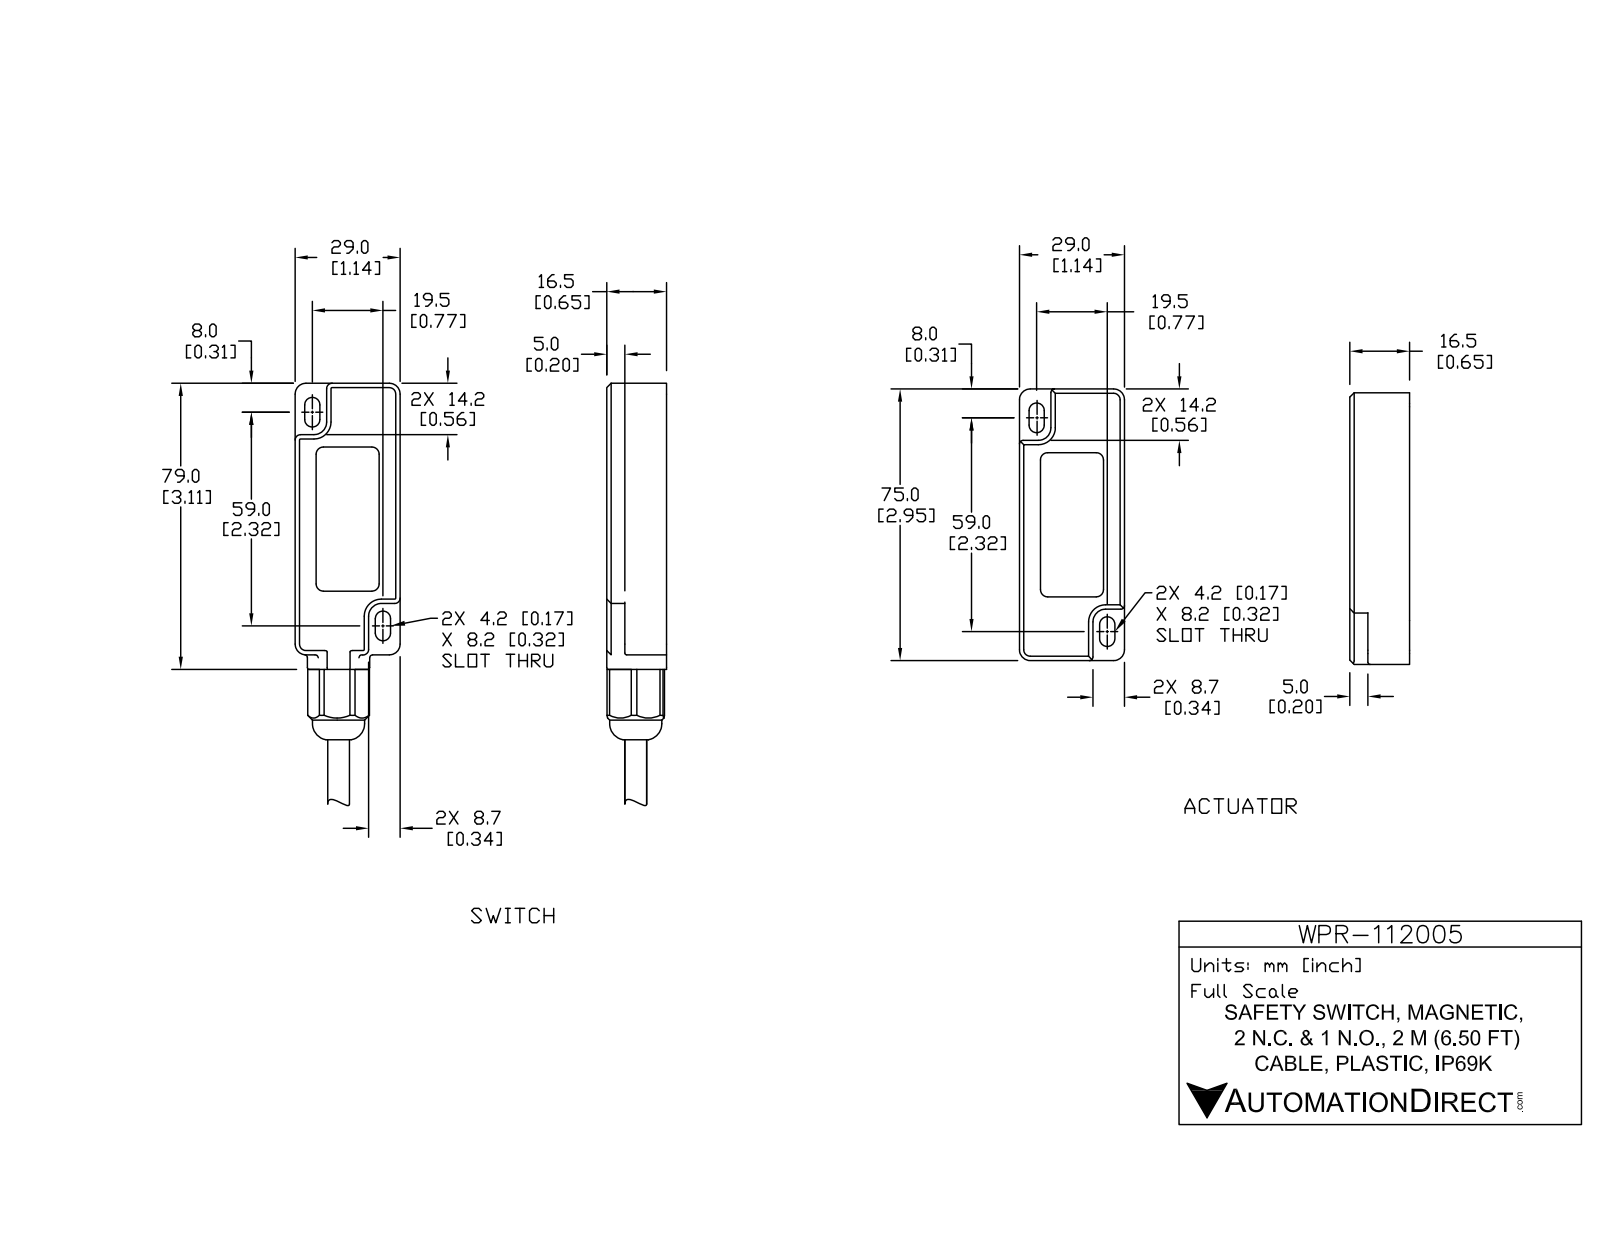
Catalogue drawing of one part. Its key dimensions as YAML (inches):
part_name: "WPR-112005_1; WPR-112005; WPR-112005_2"
step_written_by: "SolidWorks 2017 (AUTOMOTIVE_DESIGN)"
units: inches
bodies: {solids: 11, faces: 1294, planar: 573, cylindrical: 348, other: 373}
overall_size: [12.953, 2.323, 0.65]
volume: 2.63
surface_area: 65.38
round_holes:
  - {diameter: 0.195, count: 4}
  - {diameter: 0.276, count: 1}
  - {diameter: 0.327, count: 1}
  - {diameter: 0.465, count: 1}
  - {diameter: 0.472, count: 1}
round_bosses_or_shafts:
  - {diameter: 0.031, count: 8}
  - {diameter: 0.193, count: 4}
  - {diameter: 0.079, count: 4}
  - {diameter: 0.091, count: 2}
  - {diameter: 0.567, count: 1}
  - {diameter: 0.531, count: 1}
  - {diameter: 0.469, count: 1}
  - {diameter: 0.461, count: 1}
partial_cylinders:
  - {radius: 0.02, count: 85}
  - {radius: 0.039, count: 20}
  - {radius: 0.008, count: 10}
  - {radius: 0.047, count: 8}
  - {radius: 0.079, count: 8}
  - {radius: 0.083, count: 8}
  - {radius: 0.118, count: 8}
  - {radius: 0.024, count: 4}
face_to_face_distances: [0.071, 0.575, 1.181, 1.071, 0.646, 0.067, 0.571, 0.075, 0.504, 0.579]
hole_center_spacings: [2.047, 0.9, 1.459, 2.344, 2.347]
